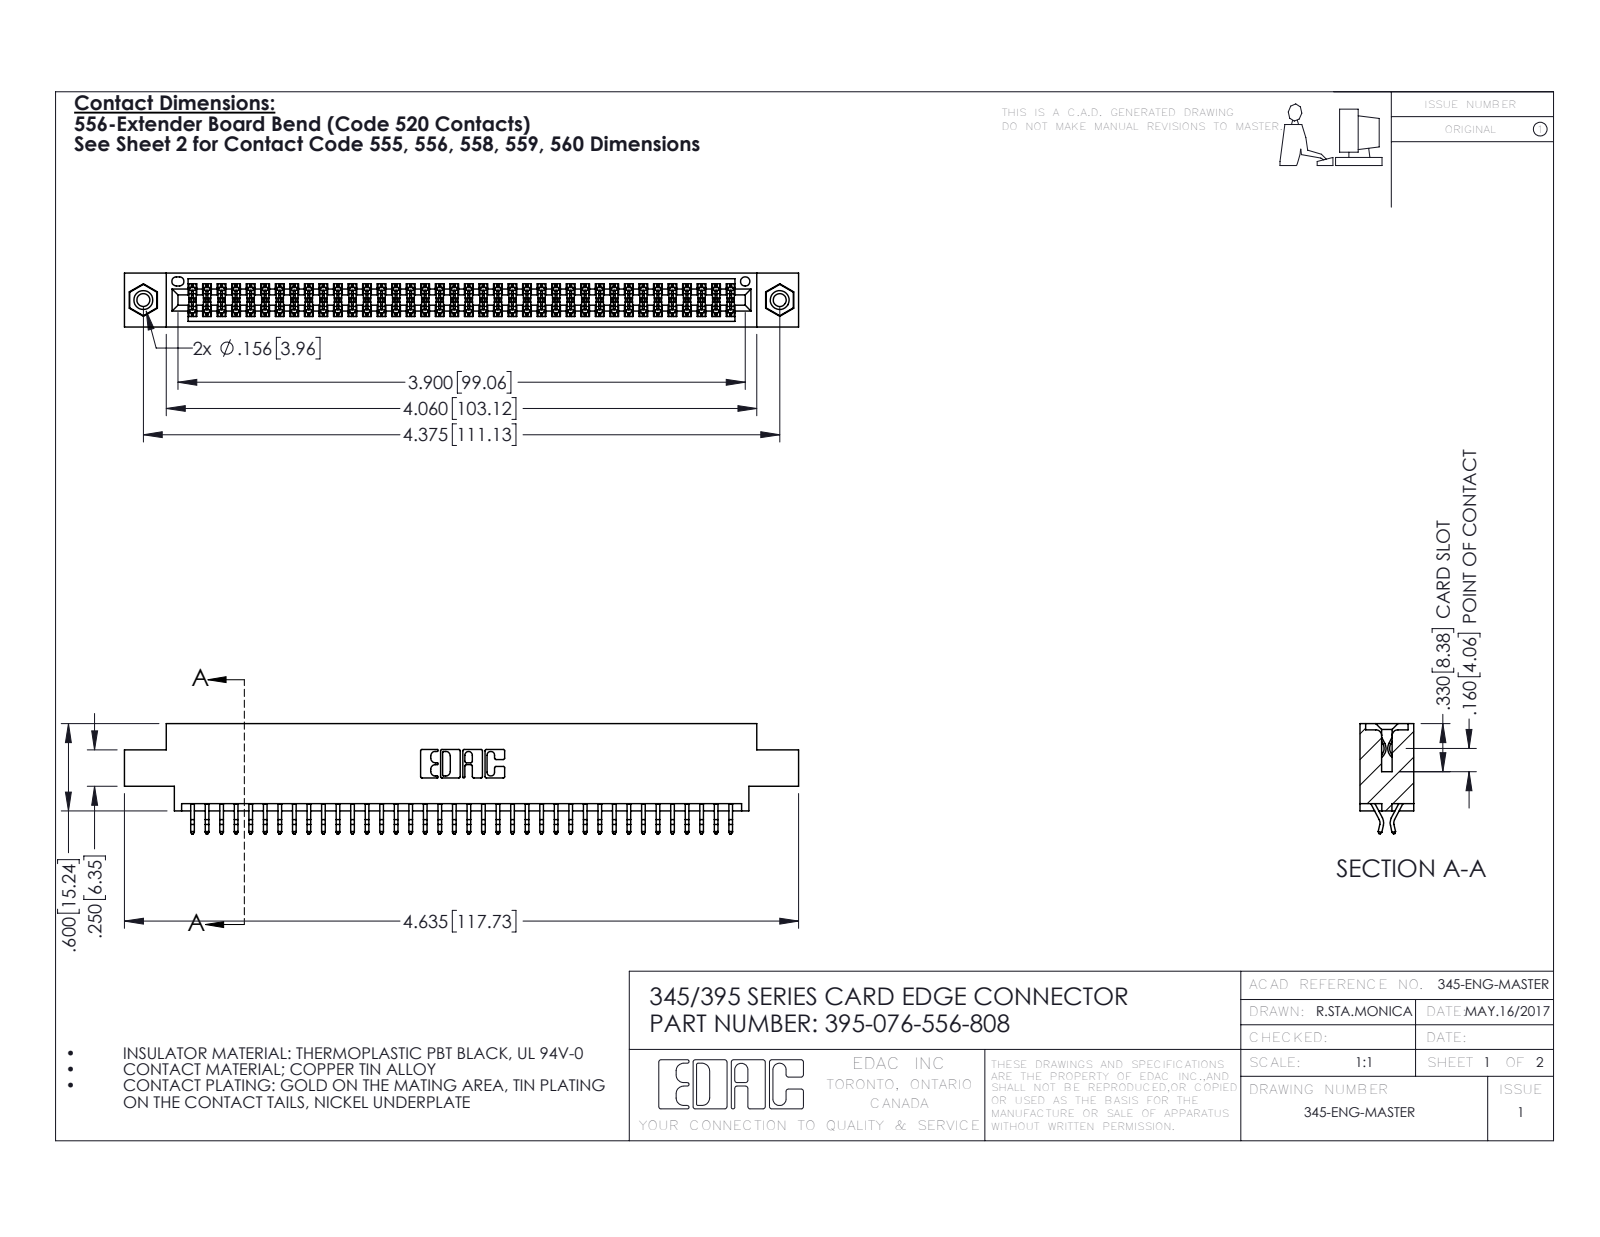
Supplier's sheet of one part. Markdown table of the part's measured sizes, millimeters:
| quantity | value |
| --- | --- |
| part name | 345 Part_0.170 Offset - 0.156 Dia-TI; 395-076-556-808; 345-292-001_556 Tail; 345-250-001_345-250-003-102 |
| STEP written by | SolidWorks 2016 (CONFIG_CONTROL_DESIGN) |
| units | millimeters |
| bodies | 79 solids, 4446 faces (2928 planar, 1502 cylindrical, 16 other) |
| overall size | 117.7 × 19.2 × 9.4 |
| volume | 11 300 mm³ |
| surface area | 16 680 mm² |
| round holes (diameter × count) | 2.3 × 2, 3.2 × 2, 4 × 2, 1.6 × 1 |
| round bosses / shafts (diameter × count) | 3.9 × 2 |
| partial cylindrical surfaces (radius × count) | 0.2 × 114, 0.3 × 22, 0.2 × 6, 0.8 × 6, 0.7 × 3, 0.3 × 2, 0.4 × 2, 0.5 × 2 |
| main face-to-face distances | 1.8, 7.6, 9.4, 5.1, 0.6, 2.5, 6.9, 5.7, 4.4, 3.8 |
| hole center spacings | 6.9, 105.1, 111.1 |
